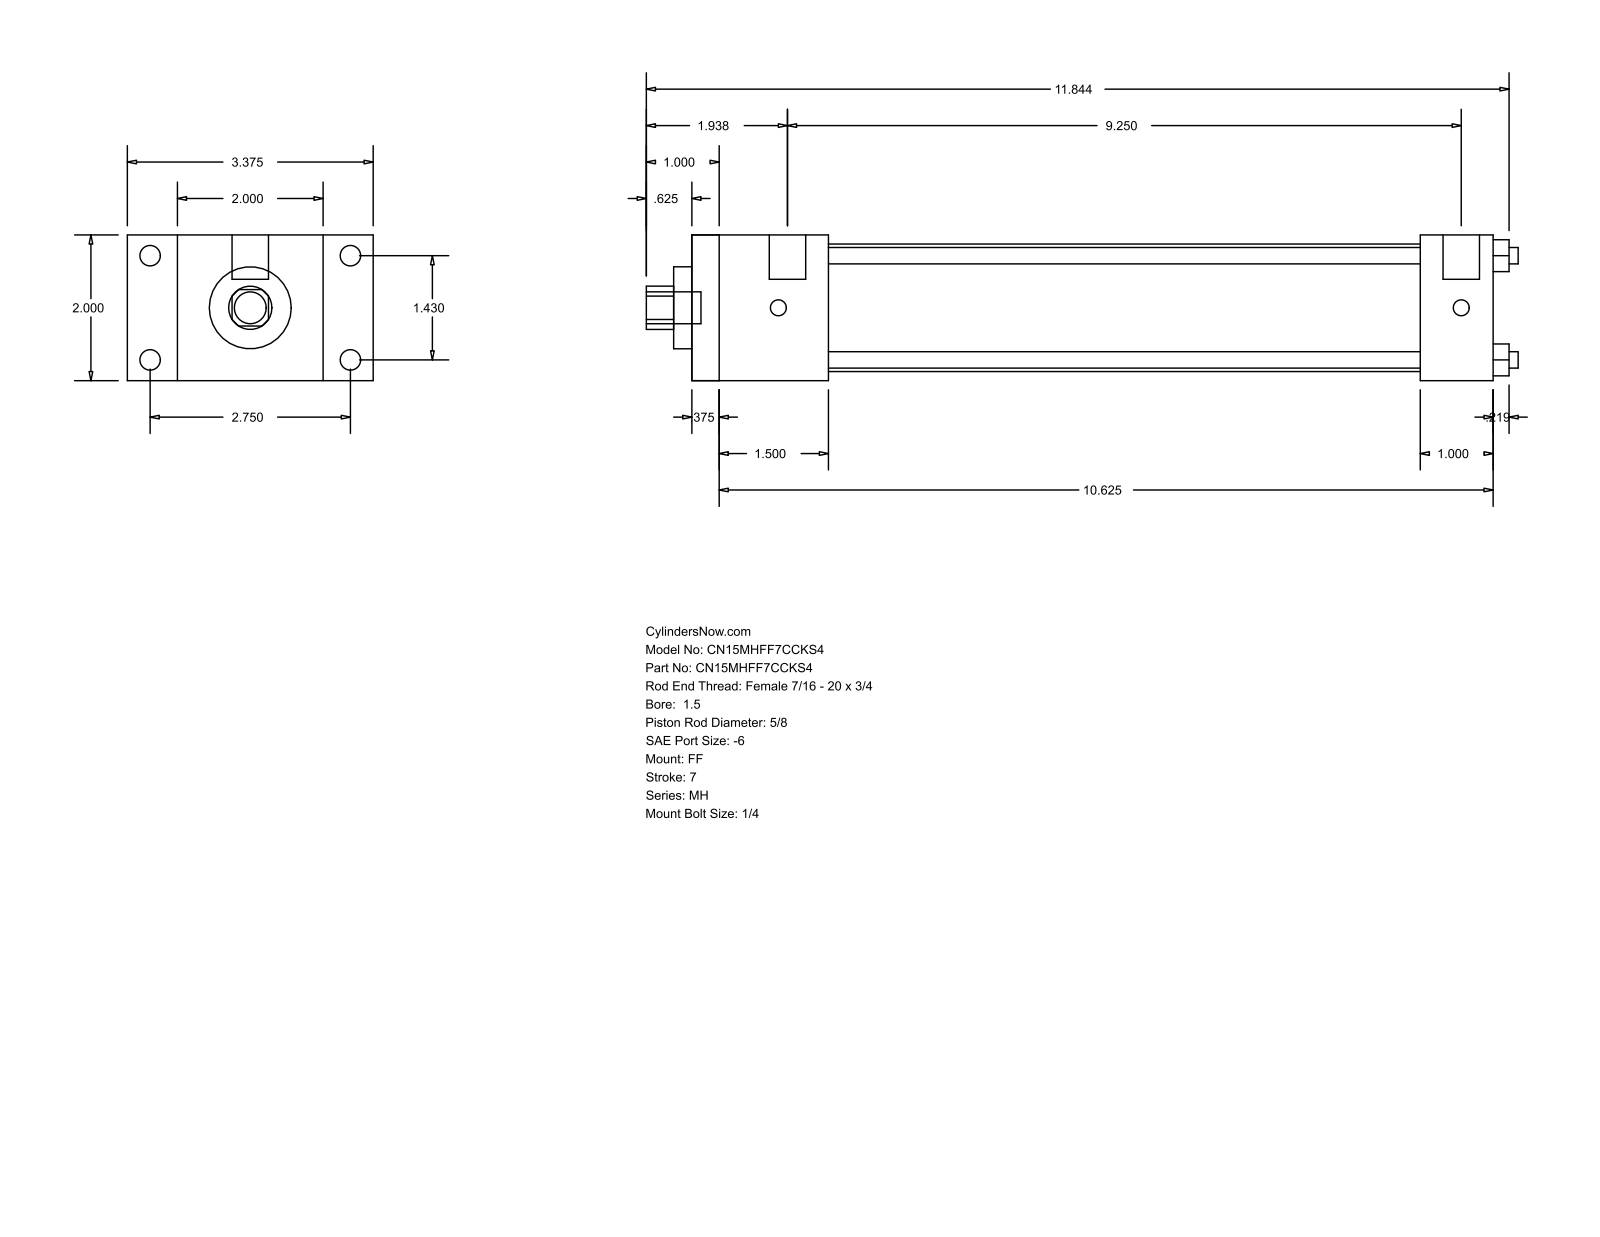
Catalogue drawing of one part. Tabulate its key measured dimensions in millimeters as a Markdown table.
| quantity | value |
| --- | --- |
| part name | MH_FF__0150_0.625 |
| STEP written by | GSSL Pune (CONFIG_CONTROL_DESIGN) |
| units | millimeters |
| bodies | 0 solids, 92 faces (64 planar, 28 cylindrical, 0 other) |
| overall size | 304.01 × 85.72 × 50.8 |
| round holes (diameter × count) | 5.71 × 4, 15.88 × 1, 28.57 × 1, 44.45 × 1 |
| round bosses / shafts (diameter × count) | 7.14 × 4, 5.56 × 4, 12.7 × 2, 11.11 × 1 |
| partial cylindrical surfaces (radius × count) | 7.54 × 1 |
| main face-to-face distances | 50.8, 279.39, 9.52, 269.87, 17.46, 68.26, 47.62, 38.1, 231.77, 254 |
| hole center spacings | 25.68, 36.32, 51.36 |
